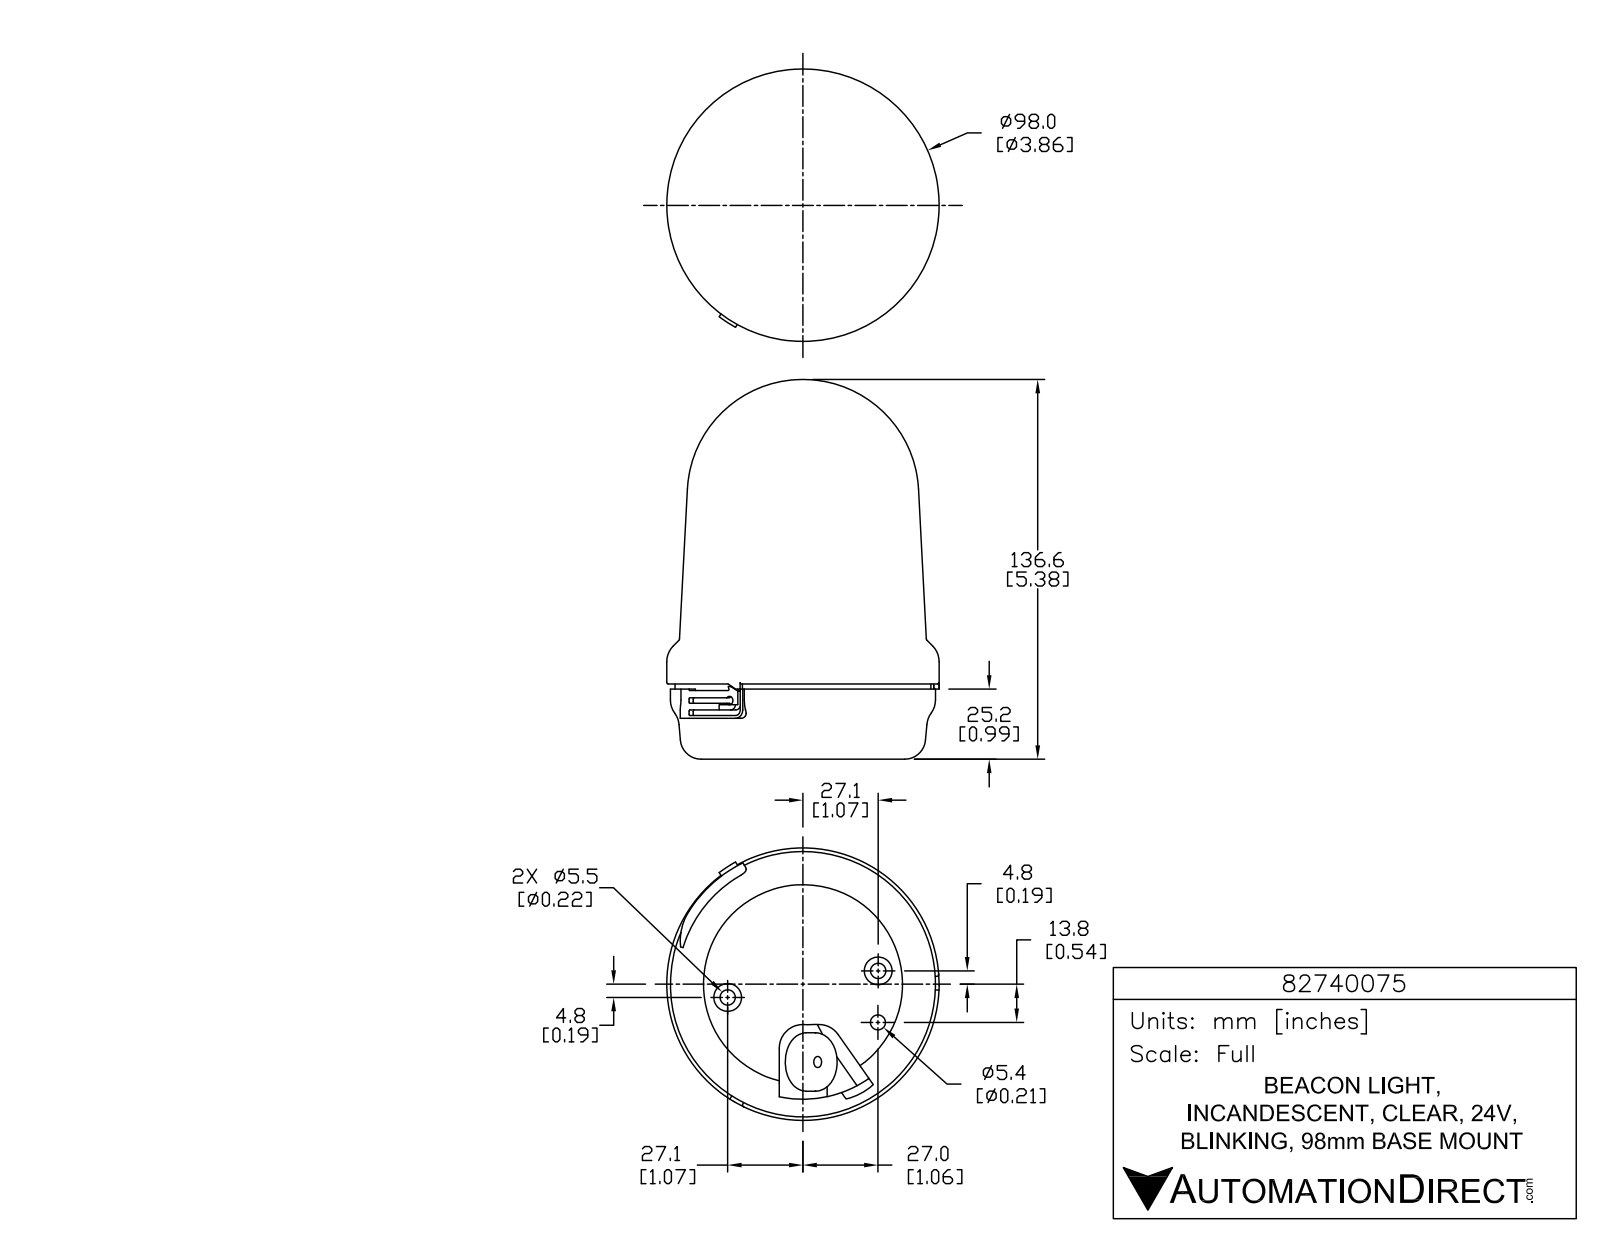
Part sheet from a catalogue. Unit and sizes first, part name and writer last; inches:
Units: inches
Overall size (bounding box): 5.378 × 3.858 × 3.858
Round holes (diameter × count): ⌀0.059 ×3, ⌀0.217 ×2, ⌀0.157 ×1, ⌀0.213 ×1, ⌀2.819 ×1
Round bosses / shafts (diameter × count): ⌀0.339 ×3, ⌀0.084 ×3, ⌀0.394 ×2, ⌀3.858 ×1, ⌀3.756 ×1, ⌀3.626 ×1, ⌀0.827 ×1
Partial cylindrical surfaces — rounded edges, fillets, slot ends (radius × count): R0.005 ×9, R0.005 ×6, R0.012 ×6, R0.012 ×6, R0.012 ×6, R0.196 ×6, R0.02 ×5, R0.039 ×4
Main face-to-face distances: 1.045, 0.972, 0.073, 0.02, 0.992, 1.065, 0.236, 0.579, 0.559, 0.413
Hole centre spacings: 1.083, 0.73, 1.193, 2.158, 2.165
Volume: 44.69 in³ · Surface area: 73.66 in²
Bodies: 1 solid, 872 faces (566 planar, 204 cylindrical, 102 other)
Part name (STEP PRODUCT): 82740075
STEP written by: SolidWorks 2015 (AUTOMOTIVE_DESIGN)
